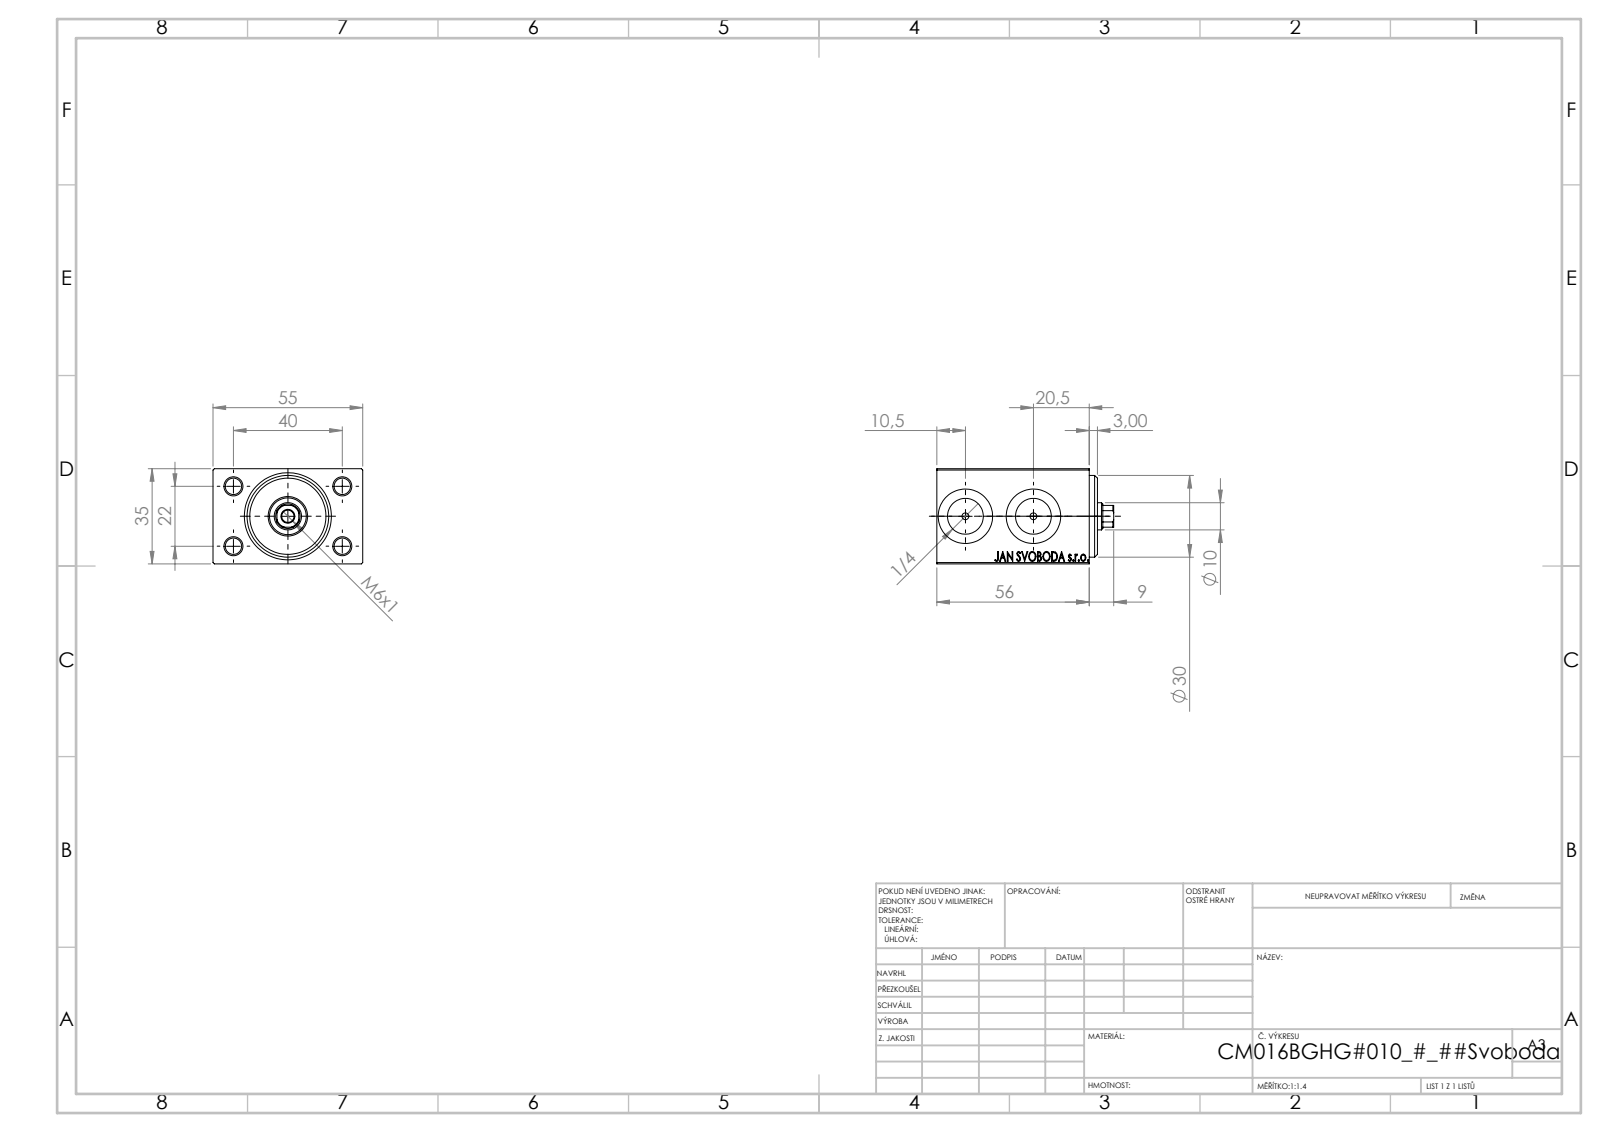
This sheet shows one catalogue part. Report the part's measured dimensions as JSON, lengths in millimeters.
{"part_name": "V450CM_B_VCP; V450CM_VC_B; V450CM_B_Body", "step_written_by": "SolidWorks 2019 (CONFIG_CONTROL_DESIGN)", "units": "millimeters", "bodies": {"solids": 3, "faces": 881, "planar": 401, "cylindrical": 54, "other": 426}, "overall_size": [65, 55, 35], "volume_mm3": 102591, "surface_area_mm2": 25030, "round_holes": [[6, 4], [2.5, 2], [13.16, 2], [20, 2], [4.5, 1], [10, 1], [13.5, 1], [14.5, 1], [16, 1], [18, 1], [30, 1]], "partial_cylinders_radius": [[4.5, 1]], "face_to_face_distances": [35, 5, 51, 55, 56, 42, 8, 3, 59, 54], "hole_center_spacings": [22.83, 22, 40, 45.65, 25]}
